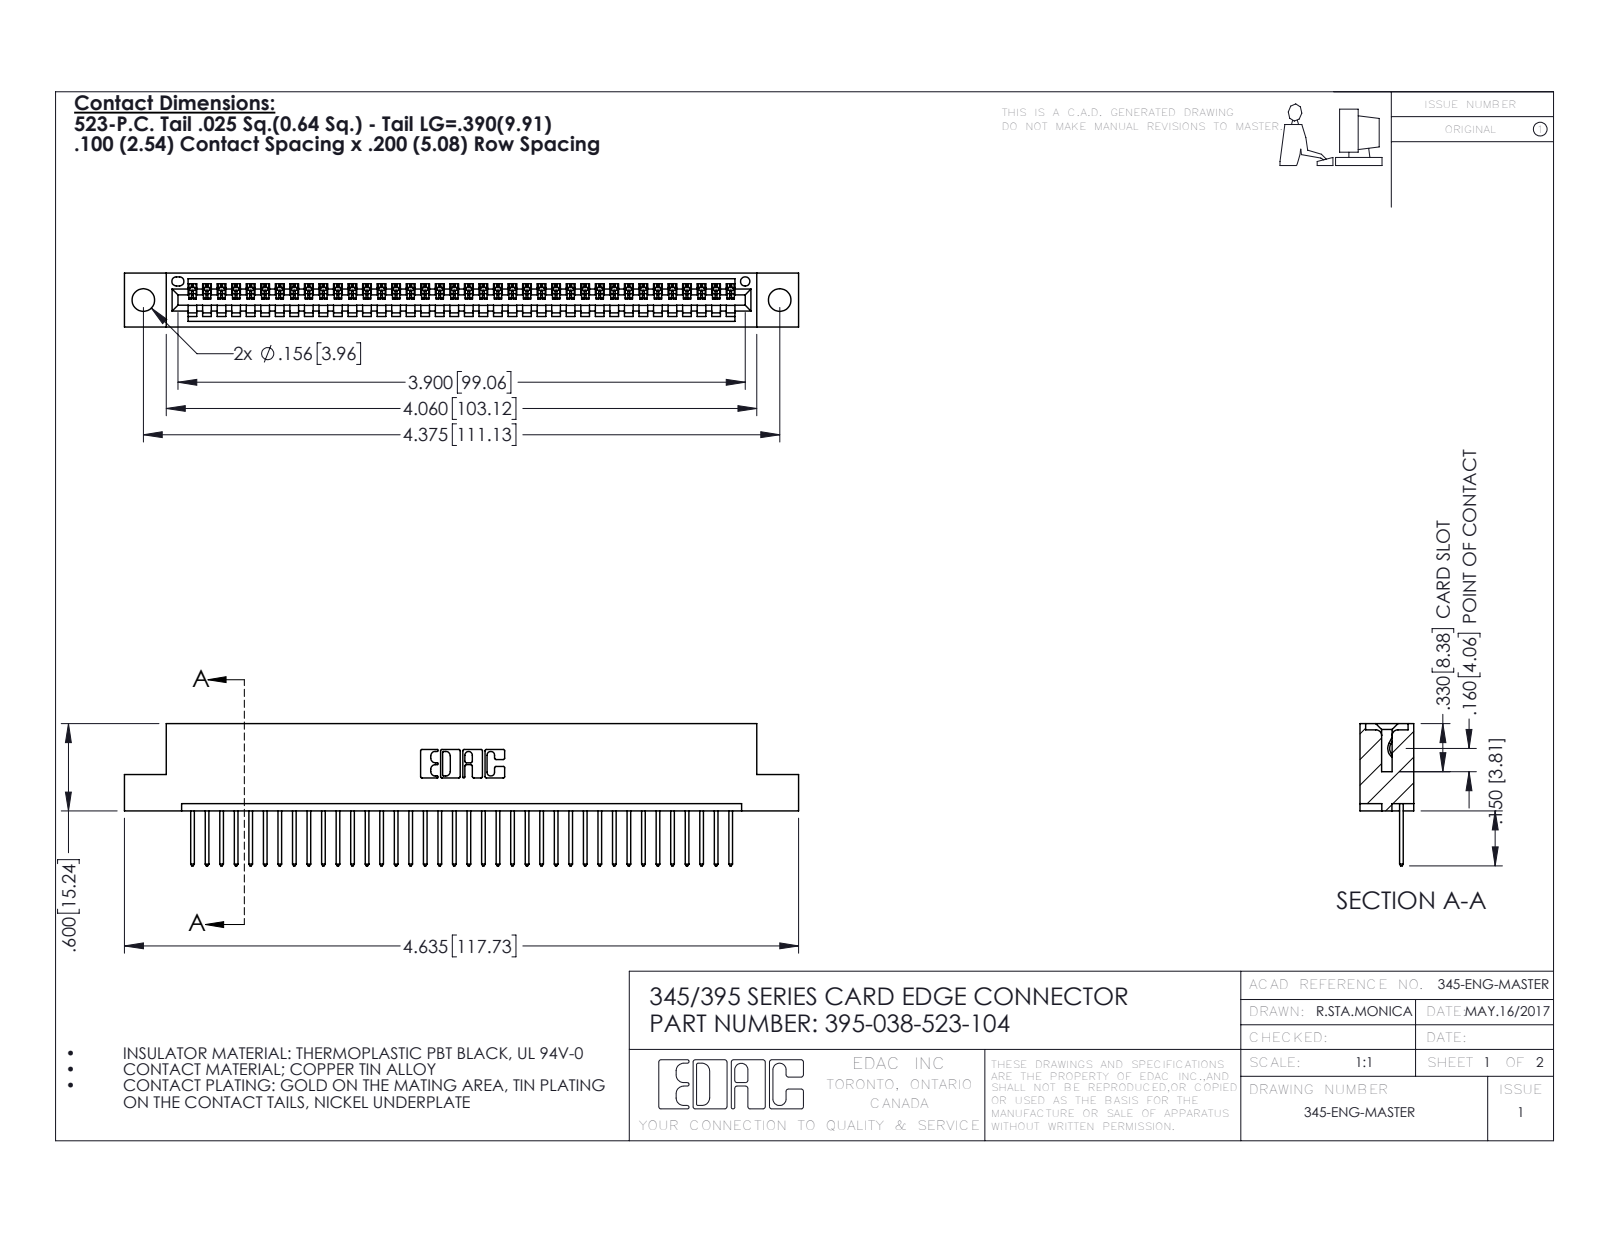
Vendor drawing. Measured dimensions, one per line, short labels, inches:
name: 345 Part_Flush Mounting Lugs - 0.156 Dia-TH; 395-038-523-104; 345-292-001_345-293-123
written by: SolidWorks 2016 (CONFIG_CONTROL_DESIGN)
unit: in
bodies: 39 solids, 2330 faces (1600 planar, 730 cylindrical, 0 other)
size: 4.635 × 0.977 × 0.37
volume: 0.674 in³; area: 22.44 in²
holes: 2× ⌀0.156, 1× ⌀0.064
rounds: 76× R0.006, 76× R0.01, 22× R0.01, 6× R0.007, 6× R0.031, 3× R0.026, 2× R0.031, 2× R0.04
face distances: 0.298, 0.072, 0.2, 0.37, 0.098, 0.272, 0.025, 0.225, 0.149, 0.072
hole spacings: 0.27, 4.139, 4.375
